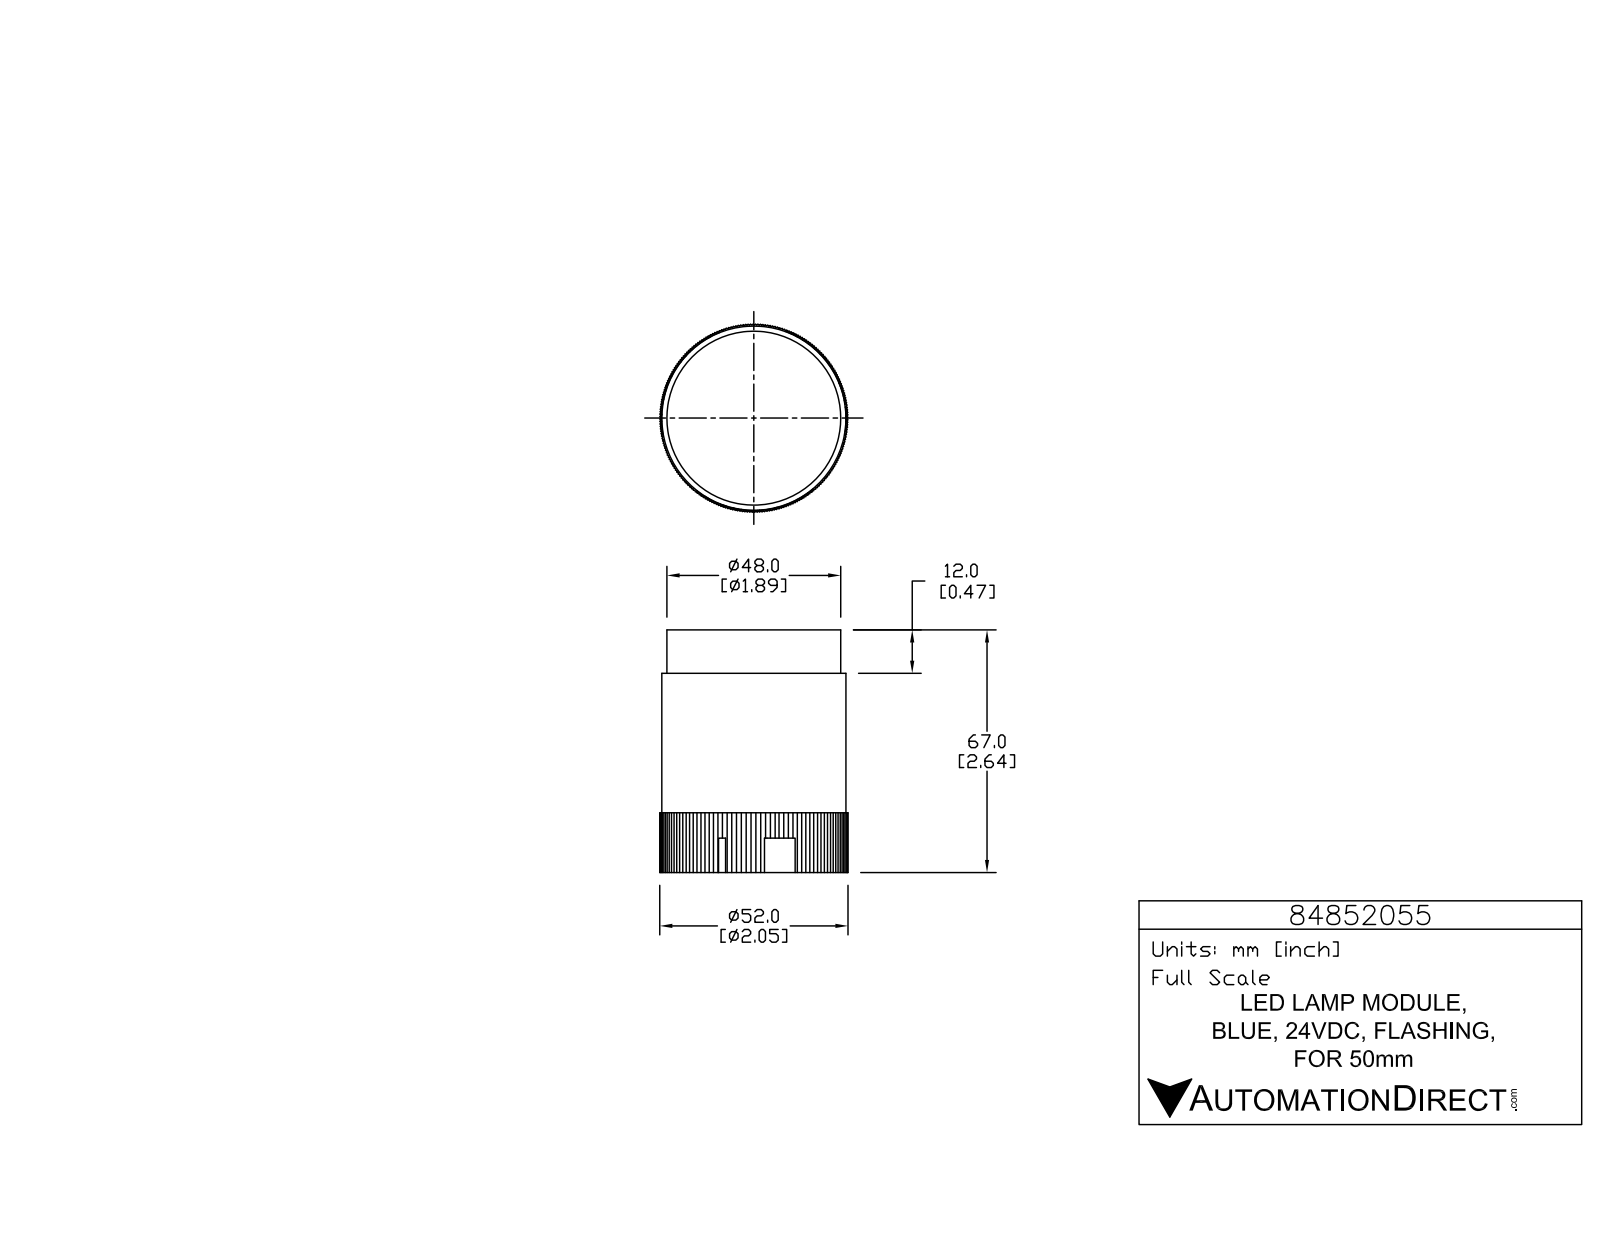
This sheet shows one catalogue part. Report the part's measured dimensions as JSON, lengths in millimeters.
{"part_name": "84852055", "step_written_by": "SolidWorks 2015 (AUTOMOTIVE_DESIGN)", "units": "millimeters", "bodies": {"solids": 1, "faces": 1265, "planar": 1020, "cylindrical": 245, "other": 0}, "overall_size": [67, 52, 52], "volume_mm3": 112600, "surface_area_mm2": 17820, "round_holes": [[1, 3], [48.2, 1]], "round_bosses_or_shafts": [[5.7, 3], [1.4, 3], [50.9, 1], [48, 1]], "partial_cylinders_radius": [[0.2, 6], [0.2, 6], [0.2, 6], [3.3, 6], [0.1, 3], [0.1, 3], [0.2, 3], [0.2, 3]], "face_to_face_distances": [55, 36.3, 36.3, 36.3, 12, 67, 36.3, 36.3, 43, 50.5]}
